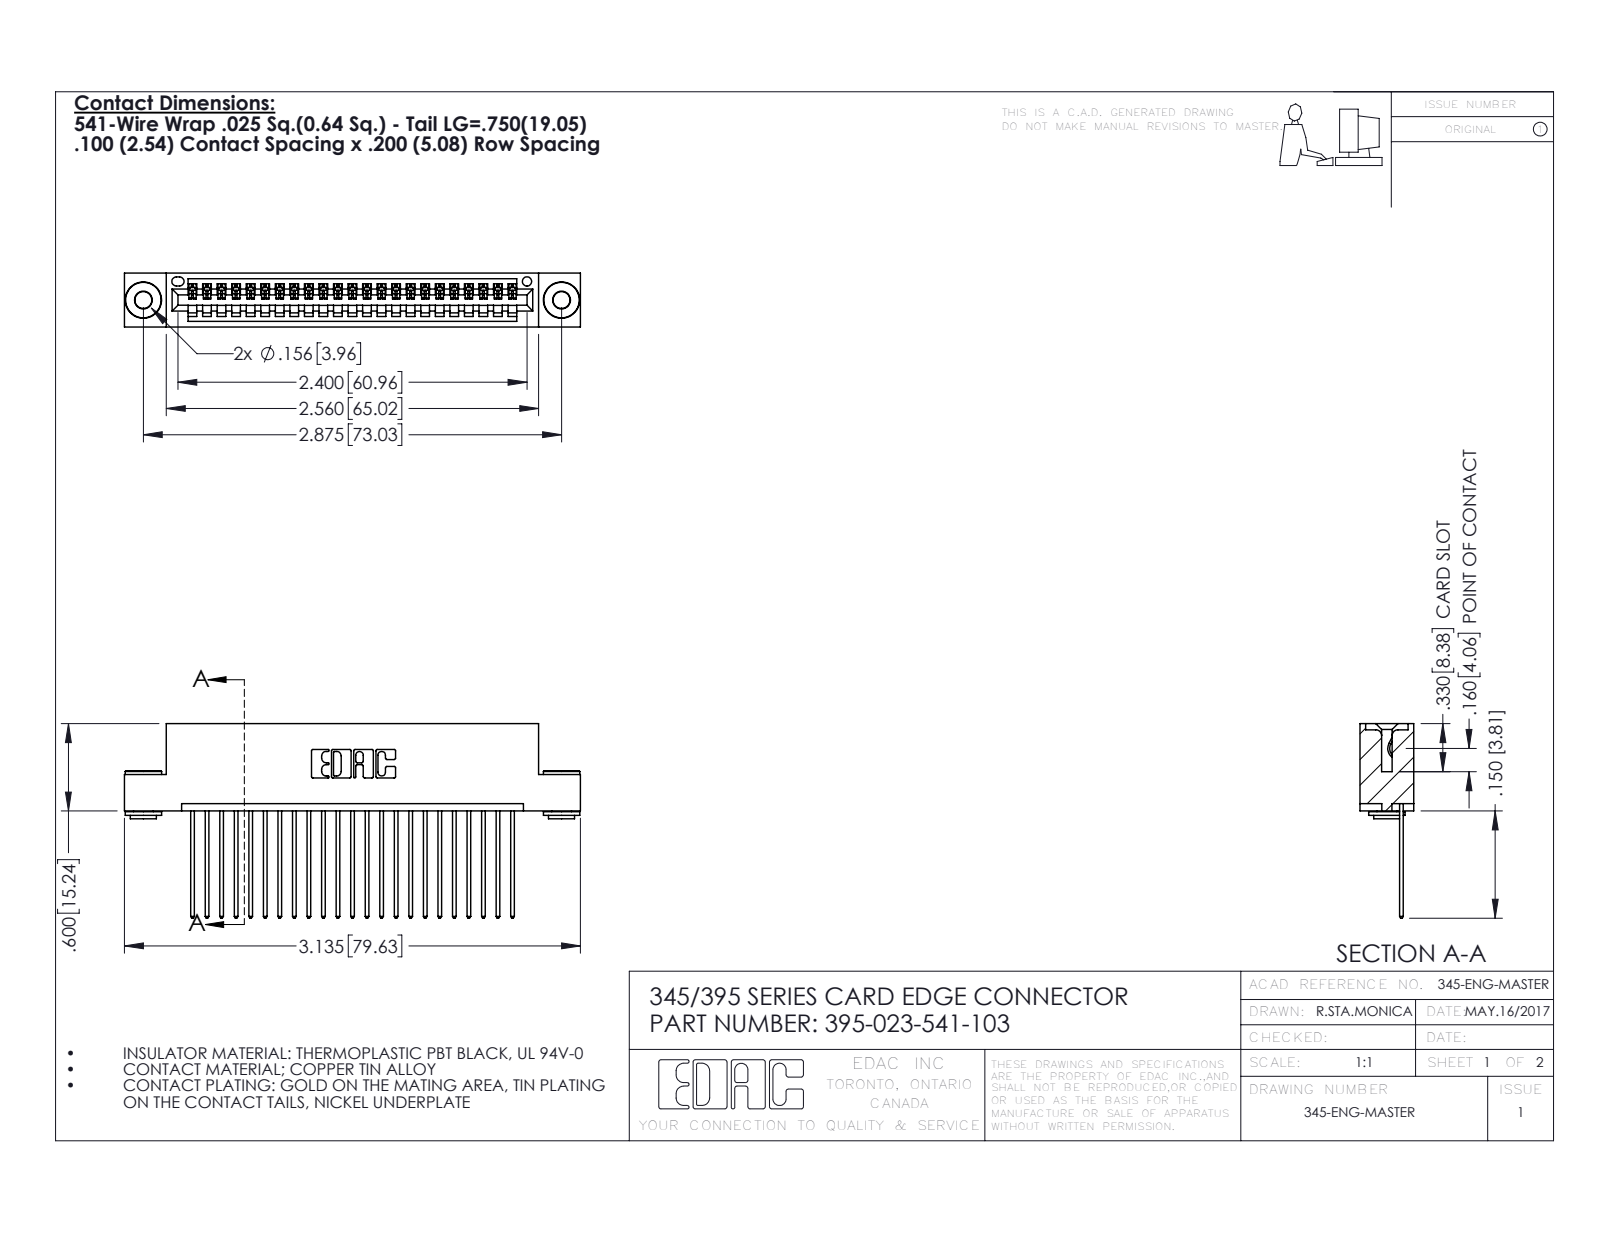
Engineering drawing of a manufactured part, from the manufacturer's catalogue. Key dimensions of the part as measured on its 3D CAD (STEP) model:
Part name (STEP PRODUCT): 395-023-541-103; 345 Part_Flush Mounting Lugs - 0.156 Dia-TH; 345-250-002_345-250-002-102; 345-292-001_345-293-141
STEP written by: SolidWorks 2016 (CONFIG_CONTROL_DESIGN)
Units: inches
Bodies: 26 solids, 1498 faces (1010 planar, 480 cylindrical, 8 other)
Overall size (bounding box): 3.135 × 1.337 × 0.37
Volume: 0.458 in³ · Surface area: 16.08 in²
Round holes (diameter × count): ⌀0.116 ×2, ⌀0.156 ×2, ⌀0.064 ×1
Round bosses / shafts (diameter × count): ⌀0.25 ×2, ⌀0.18 ×2, ⌀0.136 ×2
Partial cylindrical surfaces — rounded edges, fillets, slot ends (radius × count): R0.006 ×46, R0.01 ×46, R0.01 ×22, R0.007 ×6, R0.031 ×6, R0.026 ×3, R0.031 ×2, R0.04 ×2
Main face-to-face distances: 0.072, 0.298, 0.2, 0.025, 0.37, 0.098, 0.272, 0.225, 0.149, 0.072
Hole centre spacings: 0.27, 2.641, 2.875
